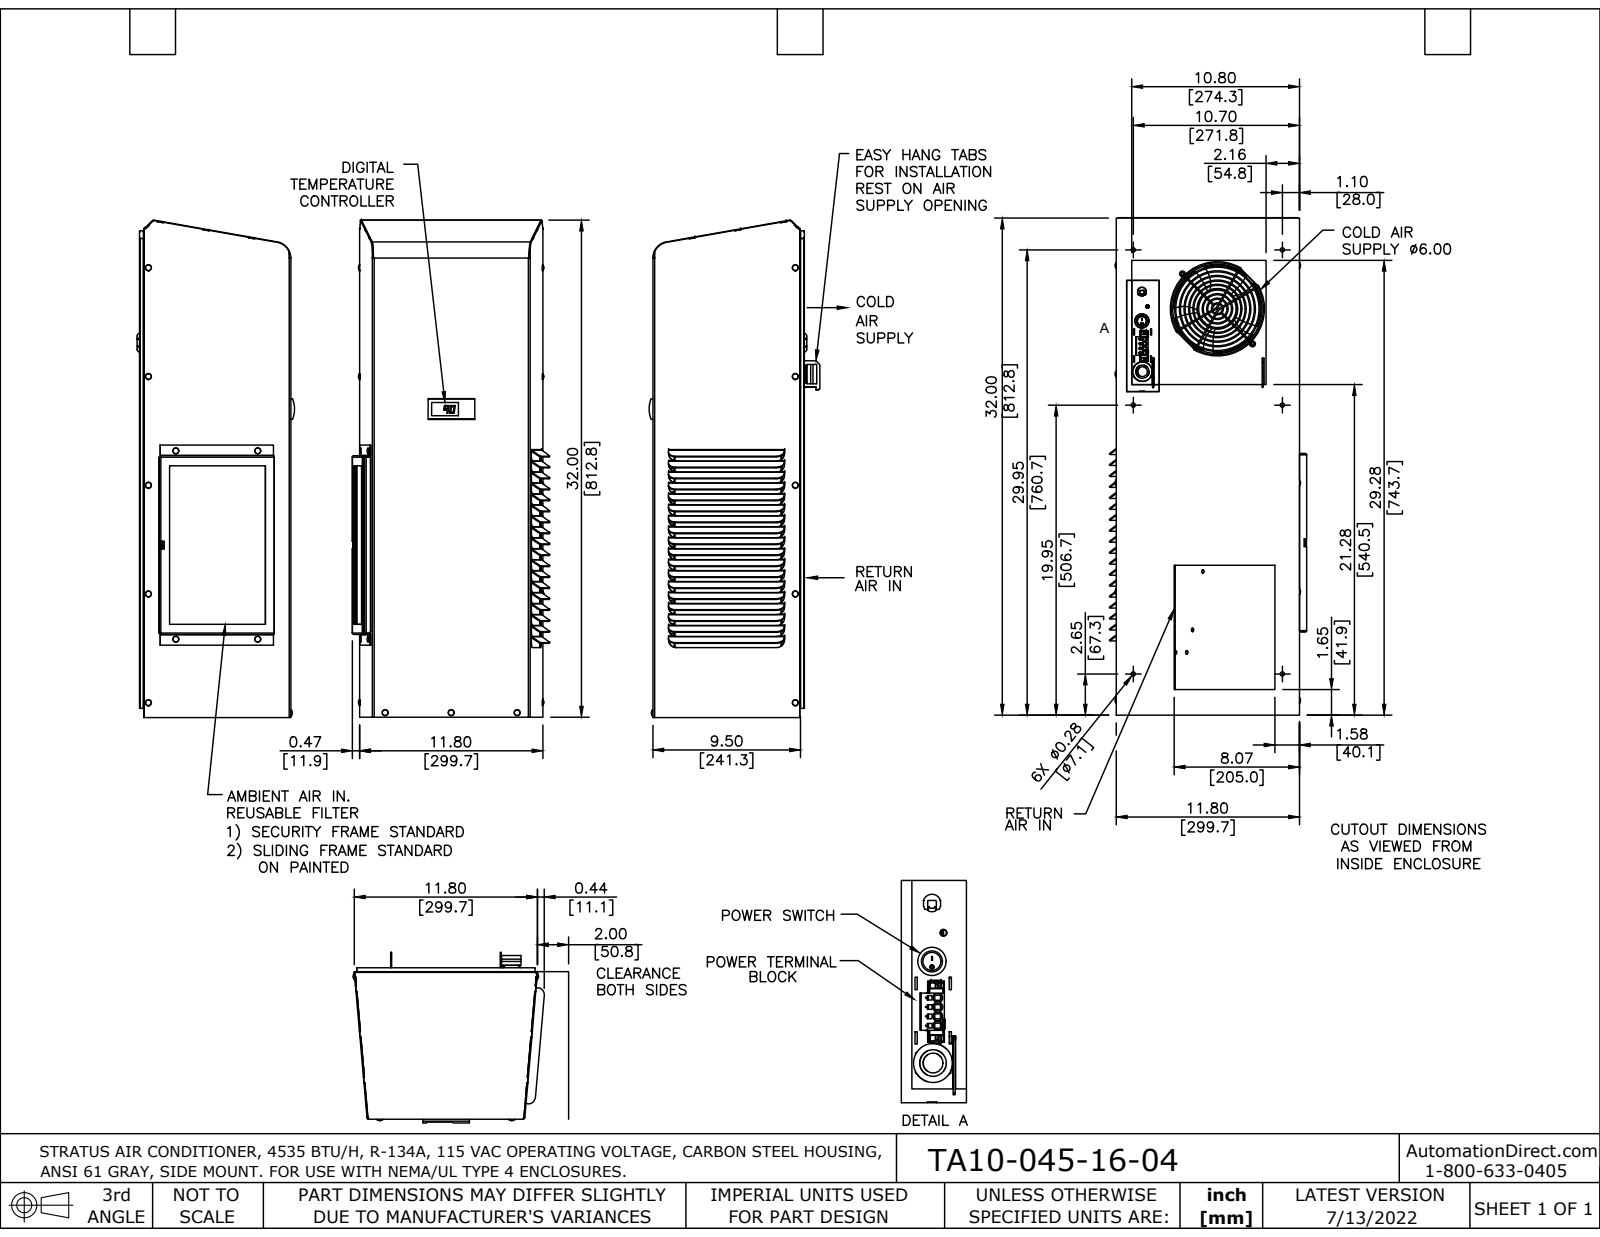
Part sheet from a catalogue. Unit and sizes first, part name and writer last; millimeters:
Units: millimetres
Overall size (bounding box): 813.4 × 319.4 × 293.3
Round holes (diameter × count): ⌀4 ×11, ⌀5.2 ×5, ⌀152.4 ×1
Round bosses / shafts (diameter × count): ⌀4.8 ×7, ⌀9.6 ×2, ⌀9 ×2, ⌀6.3 ×2, ⌀154.2 ×1, ⌀23 ×1, ⌀2.2 ×1
Partial cylindrical surfaces — rounded edges, fillets, slot ends (radius × count): R0.4 ×45, R0.3 ×42, R12.7 ×36, R12.9 ×36, R2.5 ×28, R1.5 ×21, R2.9 ×21, R0.8 ×13
Main face-to-face distances: 1.5, 239.6, 238.2, 1.5, 241.1, 2.3, 6.4, 7.8, 246, 247.5
Hole centre spacings: 177.8, 355.6, 533.4, 44, 134.6, 166.8, 307.8, 336
Volume: 2 237 000 mm³ · Surface area: 2 063 000 mm²
Bodies: 1 solid, 1743 faces (1077 planar, 496 cylindrical, 170 other)
Part name (STEP PRODUCT): TA10-045-16-04
STEP written by: SolidWorks 2021 (AUTOMOTIVE_DESIGN)
